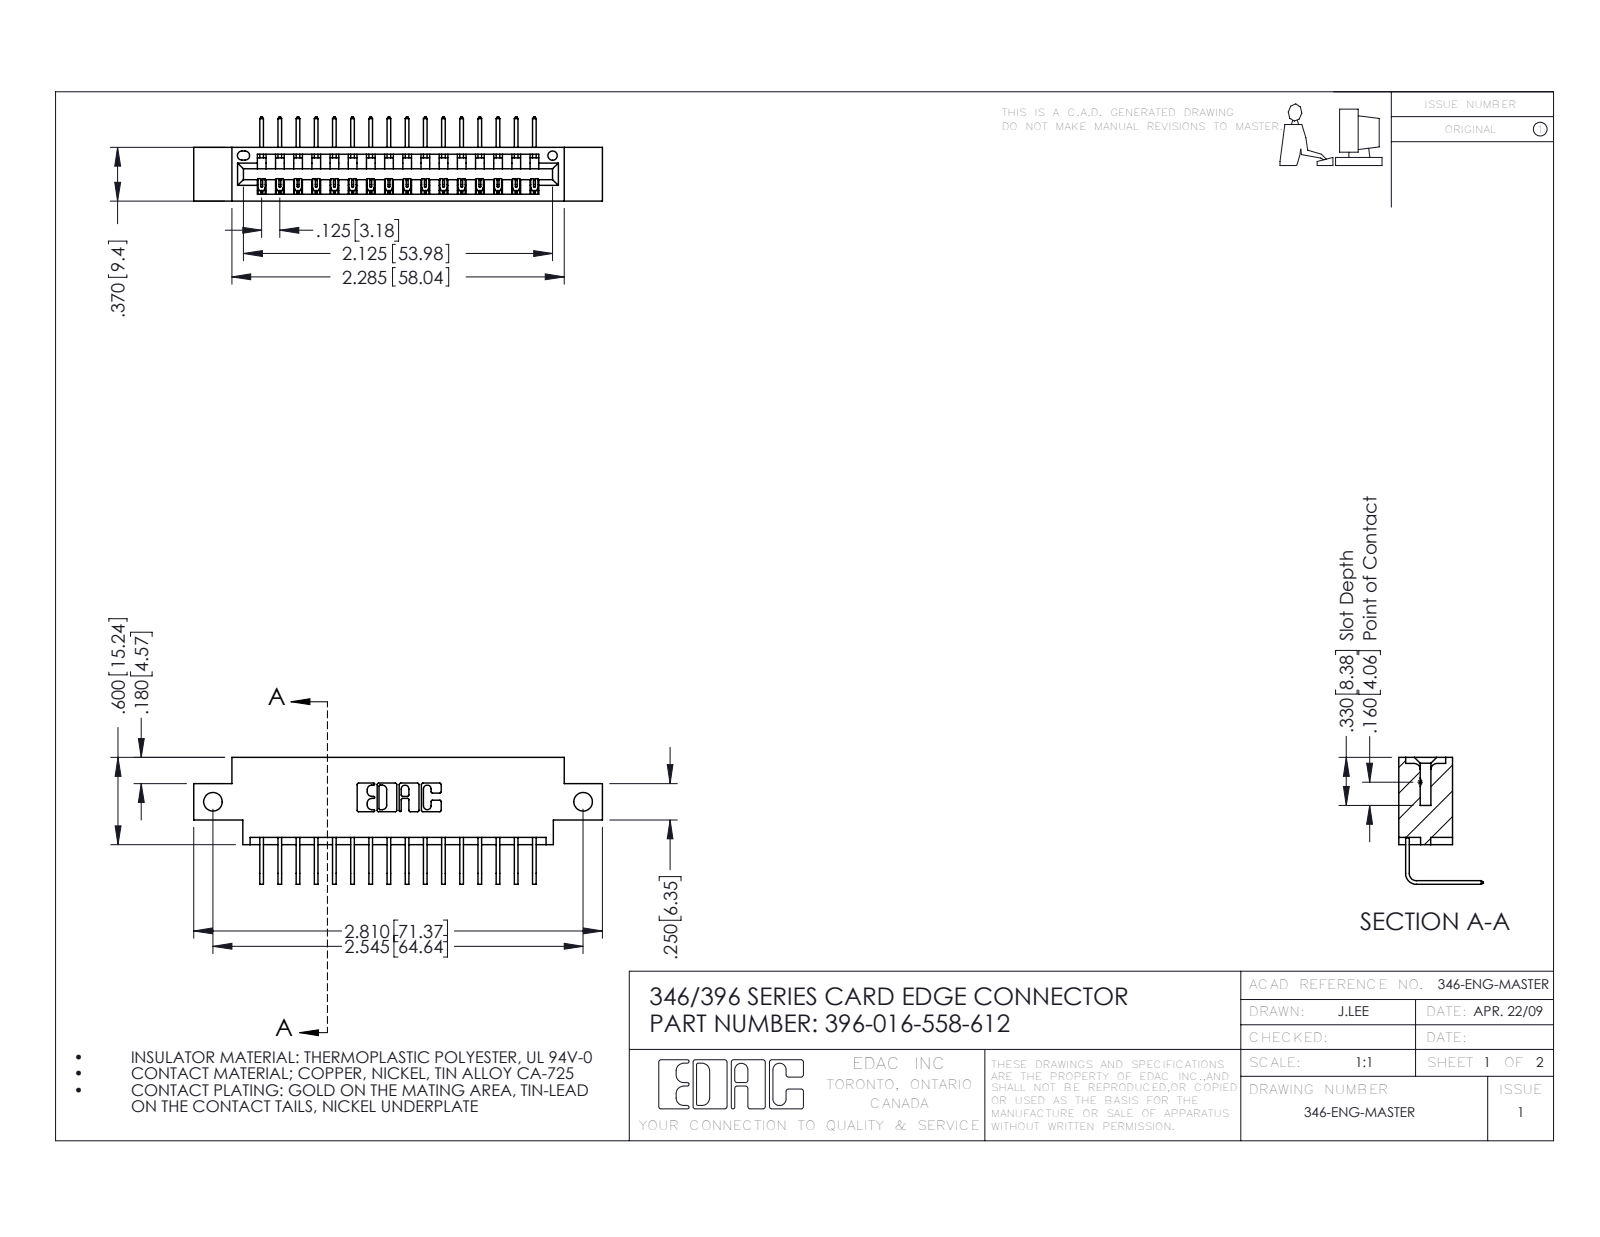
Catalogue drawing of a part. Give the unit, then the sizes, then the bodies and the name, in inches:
Units: inches
Overall size (bounding box): 2.81 × 0.873 × 0.58
Round holes (diameter × count): ⌀0.128 ×2, ⌀0.064 ×1
Partial cylindrical surfaces — rounded edges, fillets, slot ends (radius × count): R0.006 ×32, R0.01 ×22, R0.007 ×6, R0.031 ×6, R0.026 ×3, R0.031 ×2, R0.04 ×2, R0.014 ×1
Main face-to-face distances: 0.322, 0.37, 0.048, 0.25, 0.298, 0.025, 0.072, 0.148, 0.222, 0.1
Hole centre spacings: 2.545
Volume: 0.394 in³ · Surface area: 12.6 in²
Bodies: 17 solids, 1086 faces (752 planar, 334 cylindrical, 0 other)
Part name (STEP PRODUCT): 346 Part_0.170 Offset - Side Mount; 396-016-558-612; 345-292-001_558 Tail - 2
STEP written by: SolidWorks 2016 (CONFIG_CONTROL_DESIGN)
